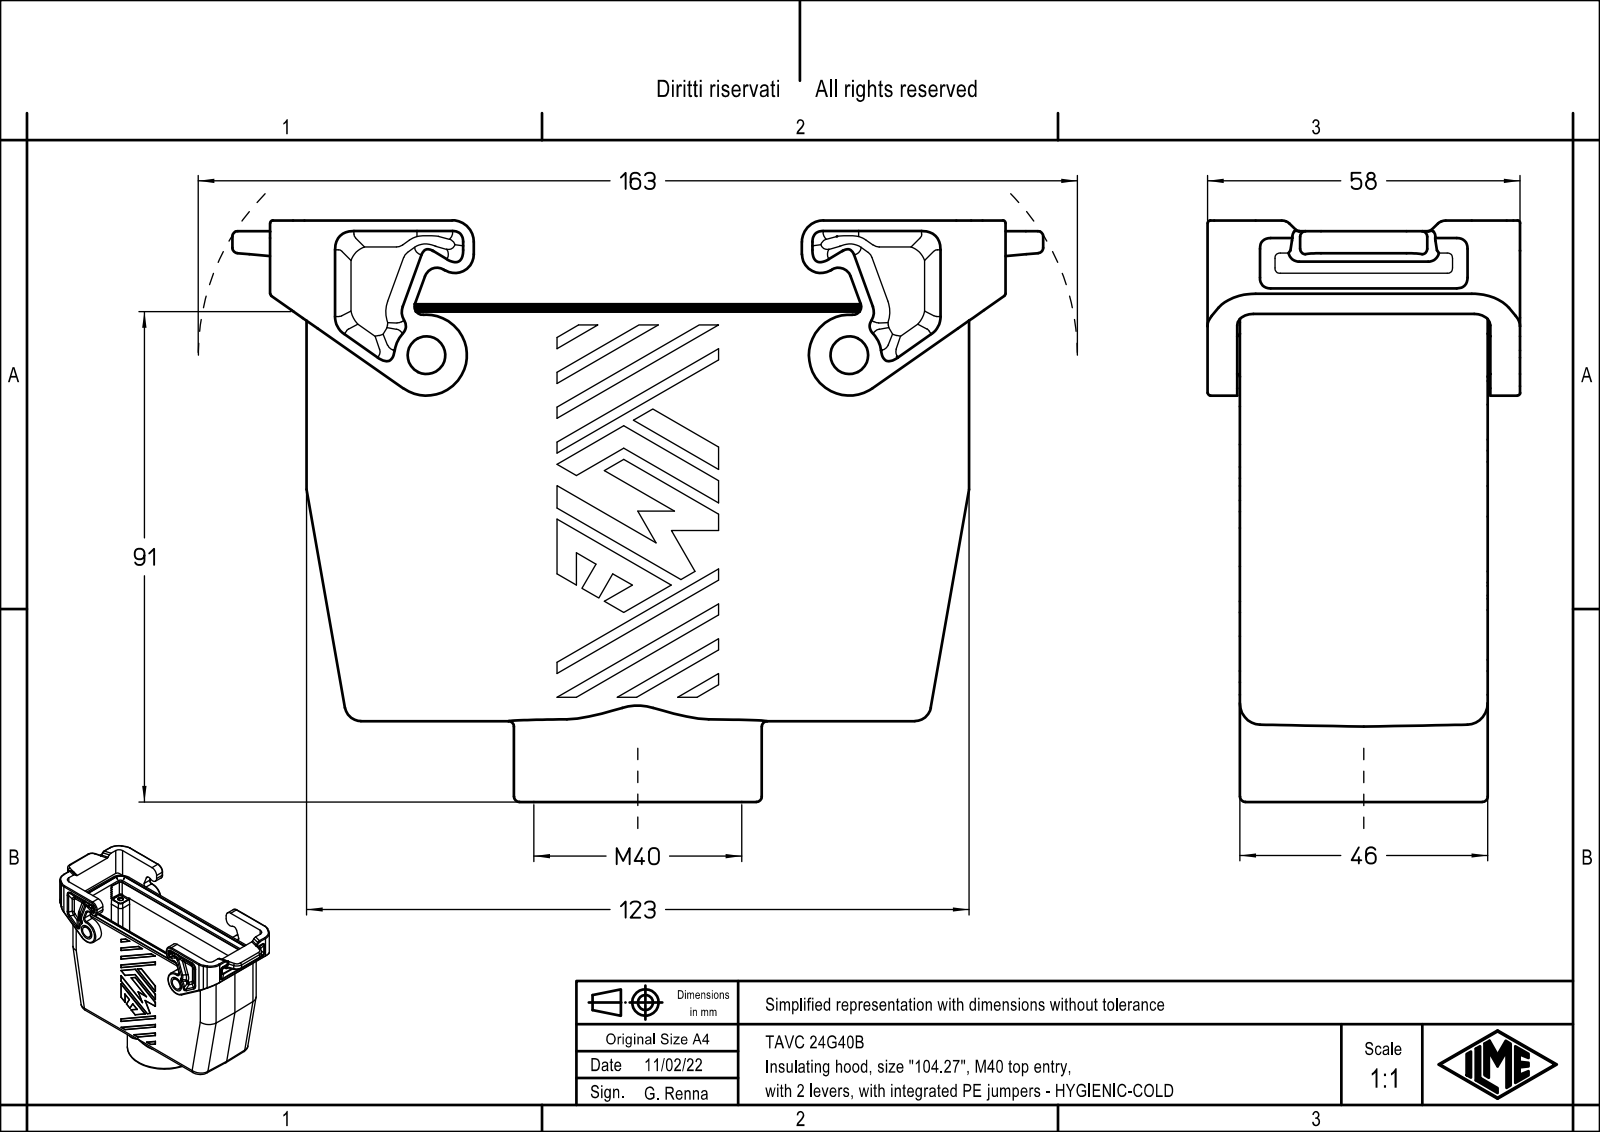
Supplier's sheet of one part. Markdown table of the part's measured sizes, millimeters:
| quantity | value |
| --- | --- |
| part name | TAVH 25 G40 |
| STEP written by | Creo Elements/Direct Modeling 20.1B 02-Apr-2019 (C) Parametric Technology GmbH (AUTOMOTIVE_DESIGN) |
| units | millimeters |
| bodies | 1 solid, 754 faces (374 planar, 318 cylindrical, 62 other) |
| overall size | 150.5 × 107.9 × 58 |
| volume | 180 382 mm³ |
| surface area | 75 685 mm² |
| round holes (diameter × count) | 3.5 × 4, 34 × 1, 38.6 × 1 |
| round bosses / shafts (diameter × count) | 7 × 2, 46 × 1 |
| partial cylindrical surfaces (radius × count) | 0.15 × 88, 2 × 20, 3 × 20, 1.5 × 18, 1 × 16, 1.3 × 12, 6 × 8, 7 × 8 |
| main face-to-face distances | 5.4, 40.6, 35.2, 46, 5.9, 0.5, 41.1, 46.5, 34.8, 6.3 |
| hole center spacings | 53.72, 27, 104, 107.45 |
